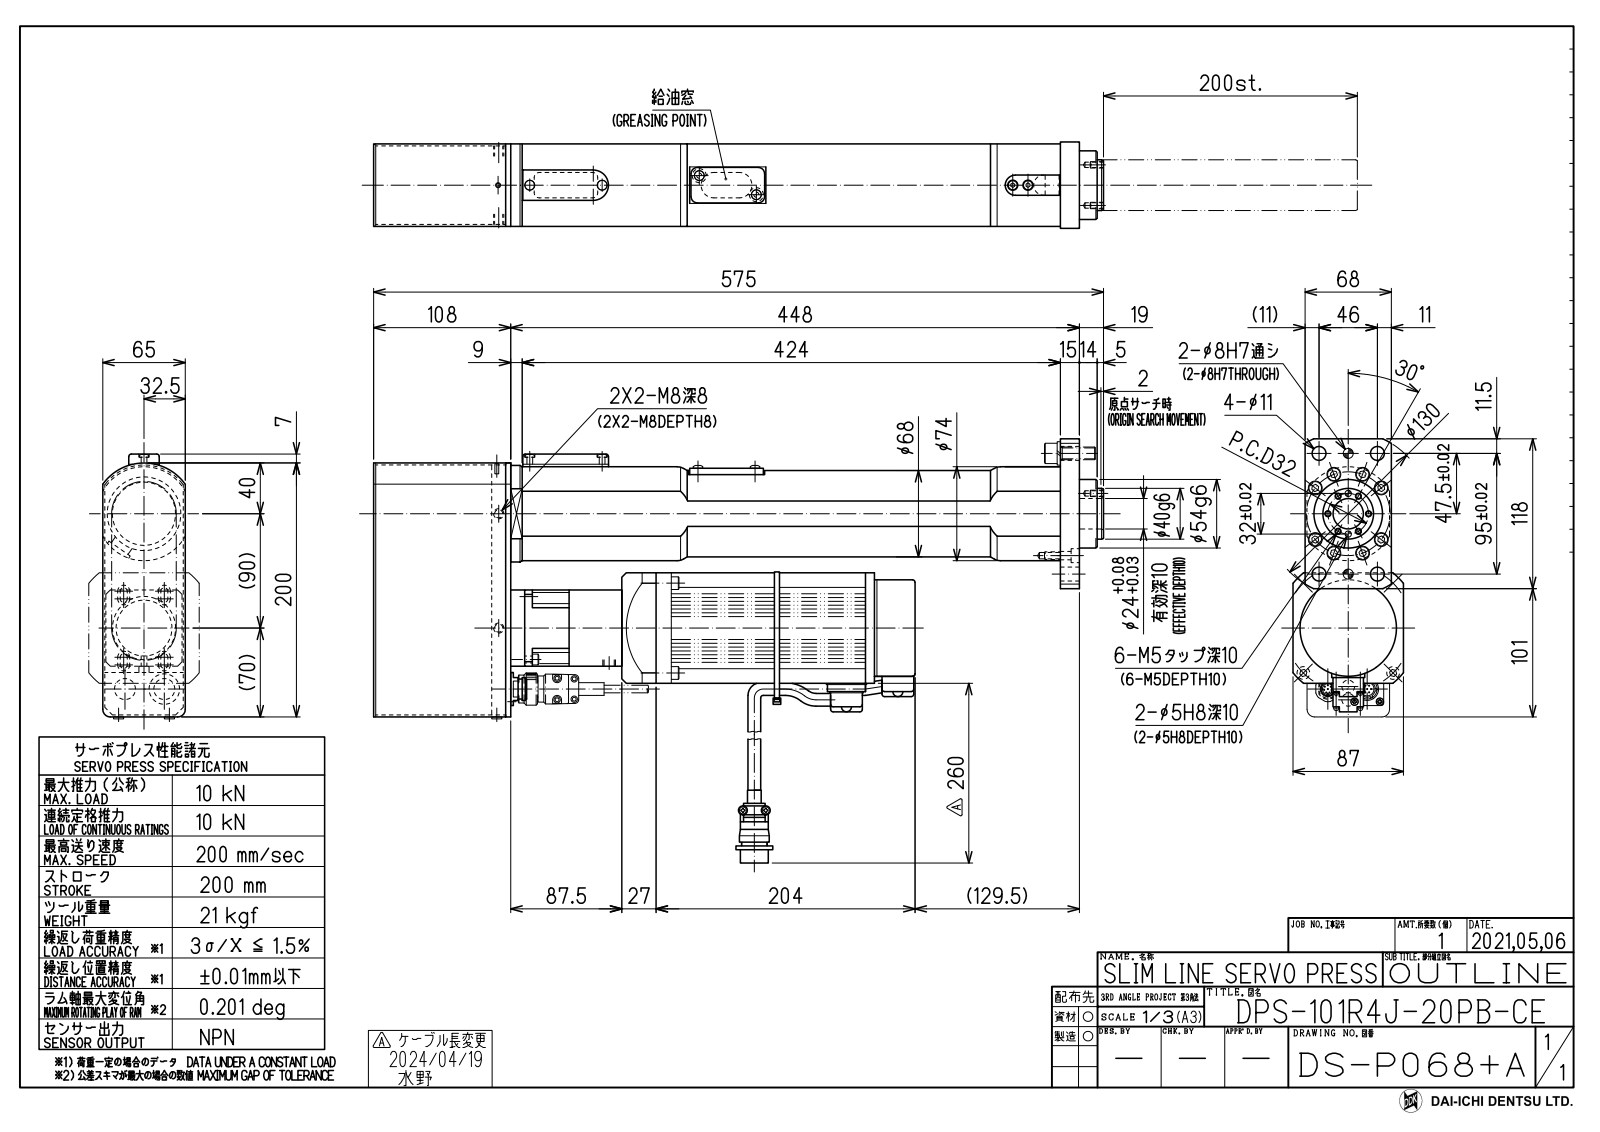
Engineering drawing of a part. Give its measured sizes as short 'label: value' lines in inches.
name: DPS-101R4J-20PB-CE_OUTLINE_20230818_簡略化_1
written by: Autodesk Inventor 2023 (CONFIG_CONTROL_DESIGN)
unit: in
bodies: 3 solids, 1062 faces (566 planar, 334 cylindrical, 162 other)
size: 22.638 × 8.622 × 3.425
volume: 304.2 in³; area: 589.8 in²
holes: 7× ⌀0.128, 6× ⌀0.163, 6× ⌀0.177, 6× ⌀0.315, 5× ⌀0.197, 5× ⌀0.433, 4× ⌀0.217, 4× ⌀0.256, 2× ⌀0.097, 2× ⌀0.335, 1× ⌀0.157, 1× ⌀0.343
bosses: 6× ⌀0.315, 4× ⌀0.335, 4× ⌀0.295, 4× ⌀0.276, 1× ⌀3.15, 1× ⌀2.677, 1× ⌀2.126, 1× ⌀1.575
rounds: 48× R0.024, 26× R0.039, 16× R0.197, 13× R0.079, 9× R0.118, 8× R0.02, 4× R0.012, 4× R0.157
face distances: 0.059, 2.559, 0.118, 0.177, 0.531, 0.433, 0.236, 0.295, 3.425, 2.992
hole spacings: 0.63, 2.403, 0.326, 0.591, 0.891, 0.906, 1.091, 1.217
